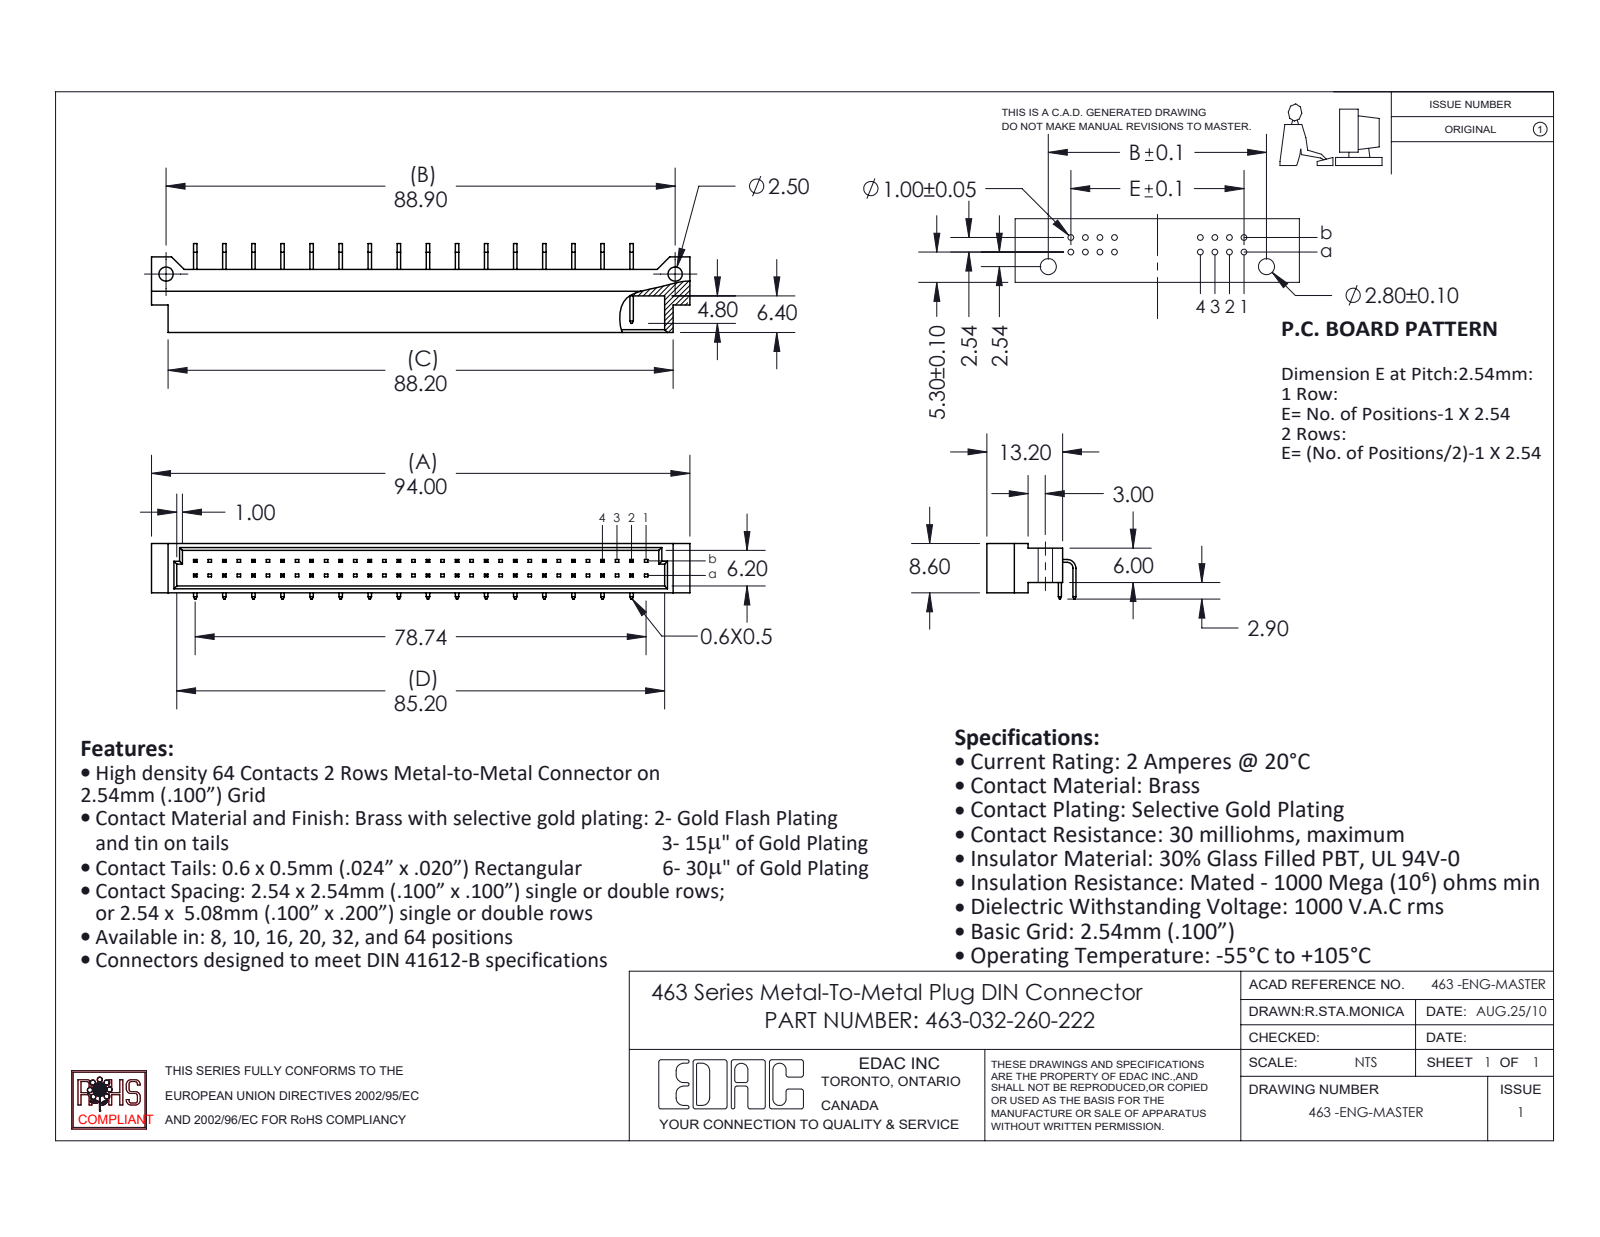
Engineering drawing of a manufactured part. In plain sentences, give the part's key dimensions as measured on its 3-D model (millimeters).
The part is named "463-032-260-222; 463-290-1; 463 Part_64; 463-290-2". Its 3-D file was written by "SolidWorks 2020 (CONFIG_CONTROL_DESIGN)". It is 33 solids with 871 faces: 803 planar, 68 cylindrical and 0 other. Overall it measures 94 by 15.53 by 9.7 millimeters. Its volume is 4 487 cubic millimeters and its surface area 6 879 square millimeters. Round holes: 2 of diameter 2.5. Partial cylindrical surfaces (rounded edges, fillets, slot ends): 2 of radius 1.02, 2 of radius 1.52. The main face-to-face distances are 1.2, 7.4, 8.6, 0.8, 6.2, 4.6, 0.5, 6, 6.8, 2.54. The hole center spacings are 88.9.
